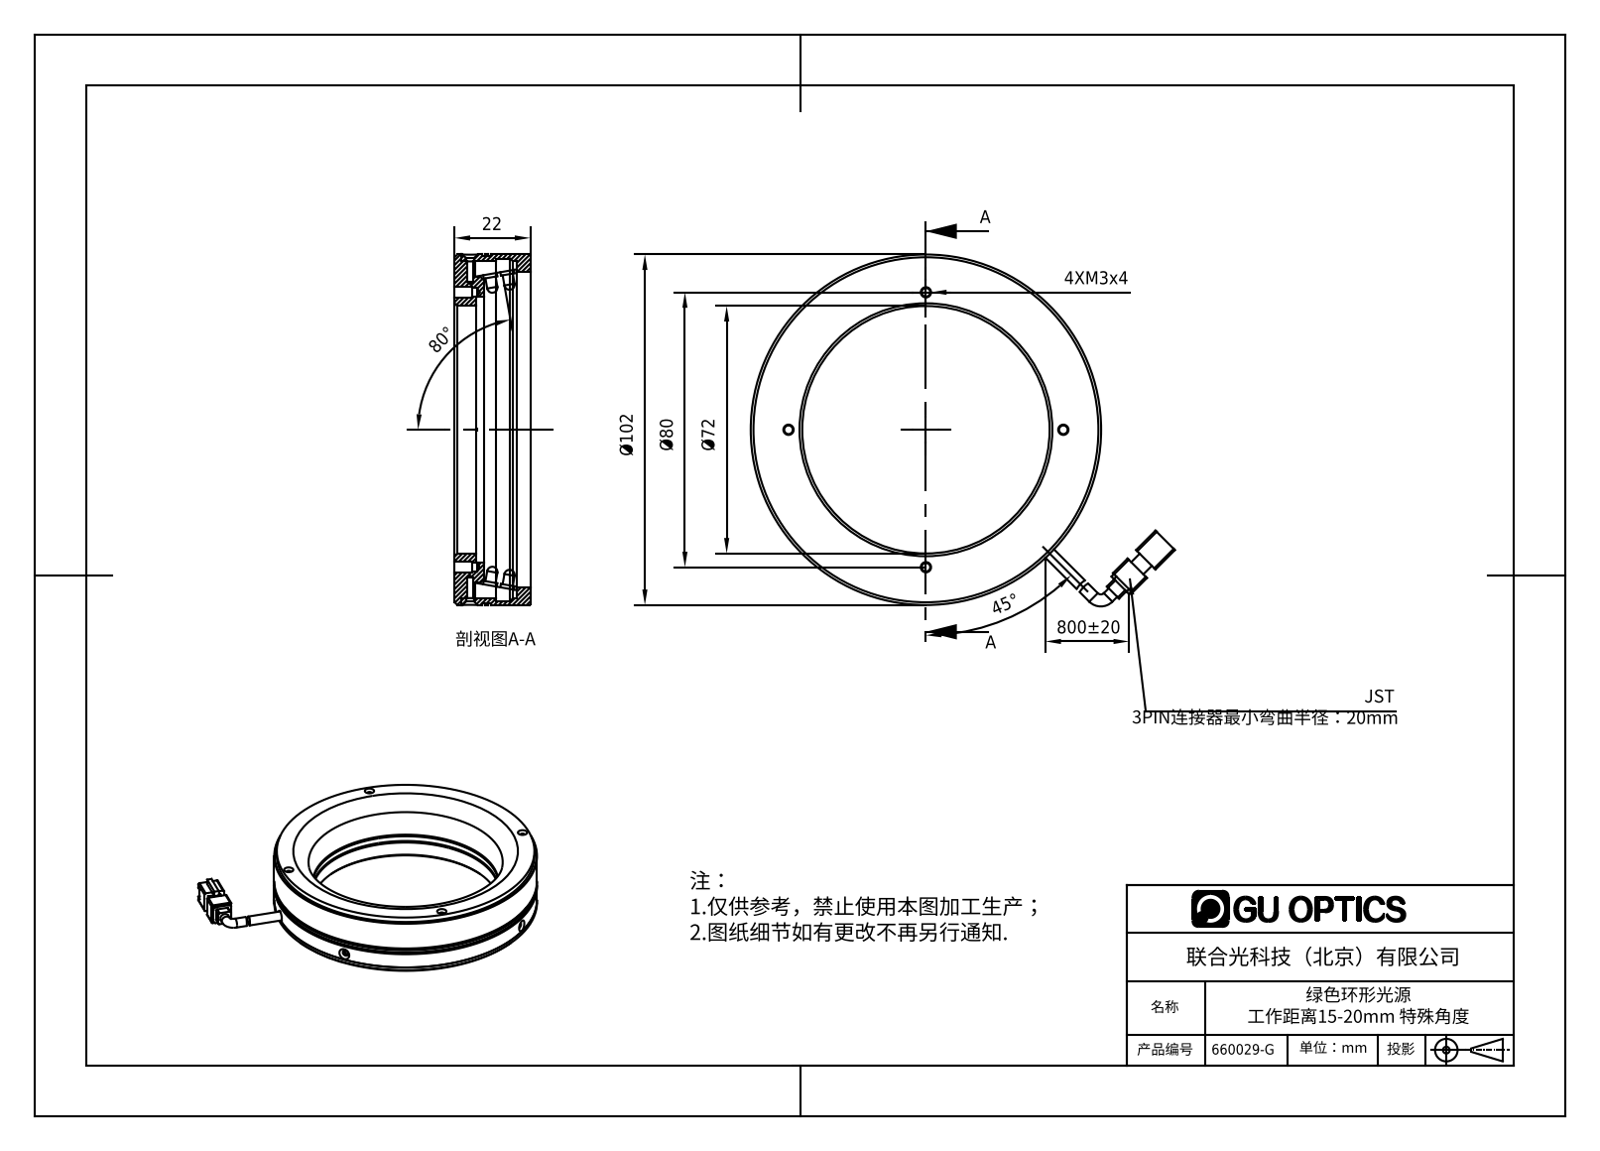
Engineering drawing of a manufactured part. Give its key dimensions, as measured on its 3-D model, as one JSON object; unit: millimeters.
{"part_name": "660029-G", "step_written_by": "SolidWorks 2016 (AUTOMOTIVE_DESIGN)", "units": "millimeters", "bodies": {"solids": 111, "faces": 2068, "planar": 1343, "cylindrical": 545, "other": 180}, "overall_size": [123.48, 102.42, 24.3], "volume_mm3": 59477, "surface_area_mm2": 60227, "round_holes": [[1.25, 4], [1.7, 4], [2.5, 4], [3, 4], [1.6, 2], [2.4, 2], [3.5, 2], [72, 1], [77.6, 1], [92, 1], [98, 1], [99.6, 1]], "round_bosses_or_shafts": [[3.8, 105], [3, 105], [3.5, 2], [102, 1], [101, 1], [100, 1], [89.11, 1], [76, 1]], "partial_cylinders_radius": [[0.5, 8], [1, 4], [1.6, 1], [7, 1]], "face_to_face_distances": [22, 2, 6, 4, 16, 18, 24, 2.5, 12, 1], "hole_center_spacings": [34.2, 80.89, 40, 47.5, 56.57, 67.18, 80, 95.01]}
